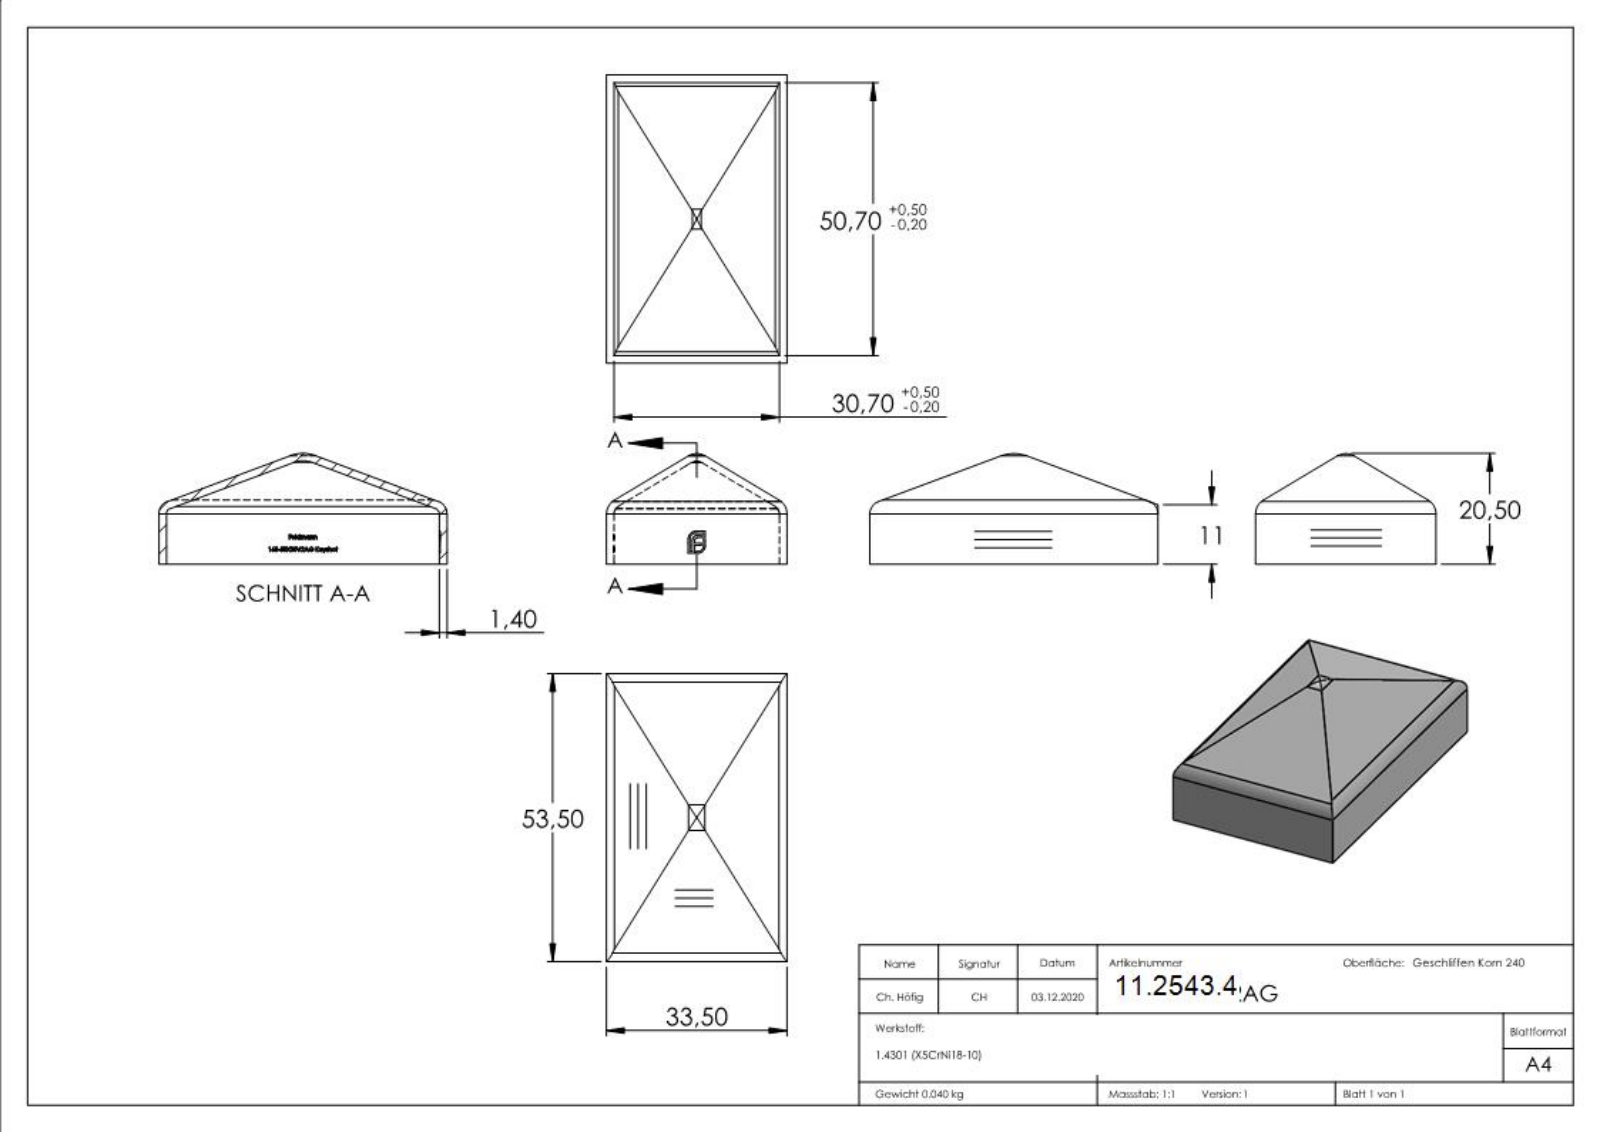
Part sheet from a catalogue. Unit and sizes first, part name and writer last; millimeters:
Units: millimetres
Overall size (bounding box): 53.5 × 33.5 × 20.5
Partial cylindrical surfaces — rounded edges, fillets, slot ends (radius × count): R1.6 ×3, R3 ×3, R1.05 ×2, R2.45 ×2, R5.35 ×1, R6.75 ×1
Main face-to-face distances: 1.4, 32.1, 52.1, 33.5, 30.7, 53.5, 50.7, 1.3, 50.8, 52.2
Volume: 5 039 mm³ · Surface area: 7 452 mm²
Bodies: 1 solid, 344 faces (188 planar, 16 cylindrical, 140 other)
Part name (STEP PRODUCT): 165-50X30V2AG
STEP written by: SolidWorks 2018 (CONFIG_CONTROL_DESIGN)
